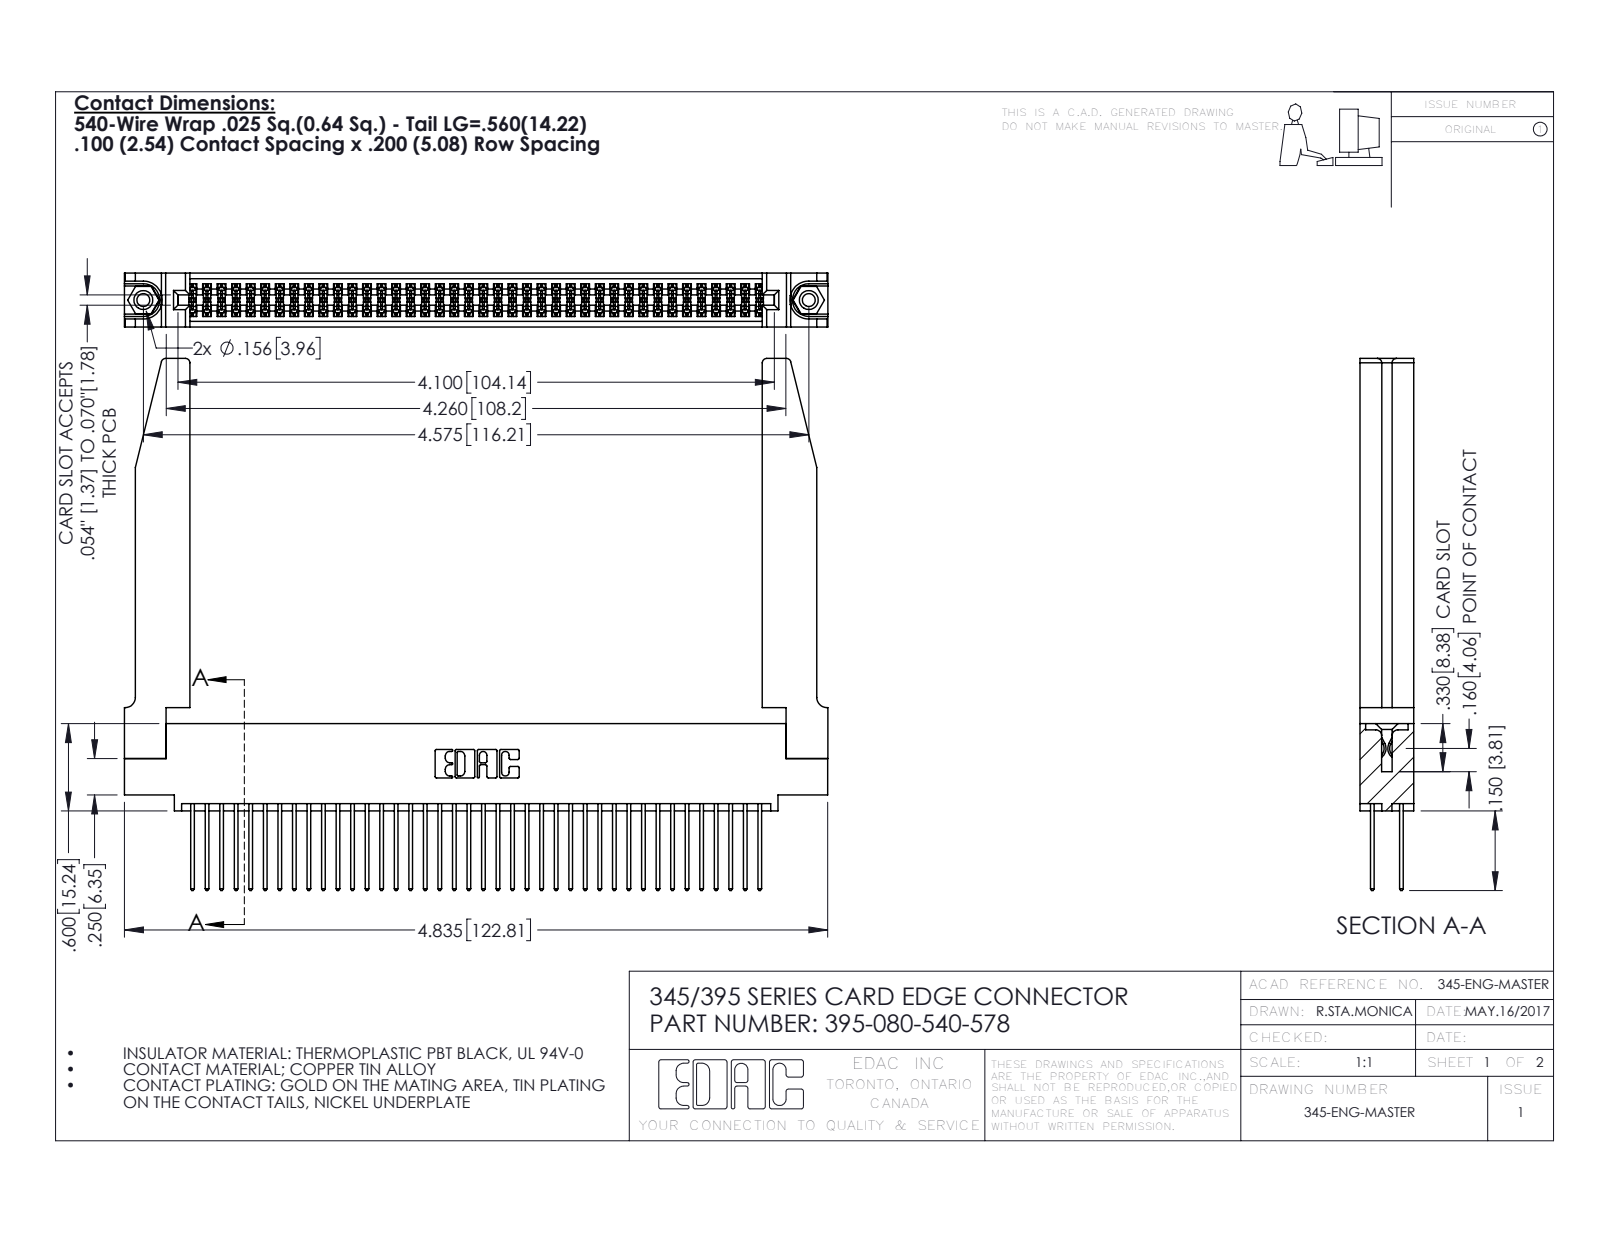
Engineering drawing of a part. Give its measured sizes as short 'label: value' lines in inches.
name: 395-080-540-578; 345 Part_0.110 Offset - 0.156 Dia-TH; 345-220-078_345-220-078; 345-292-001_345-293-140 (+1 more)
written by: SolidWorks 2016 (CONFIG_CONTROL_DESIGN)
unit: in
bodies: 85 solids, 4364 faces (2866 planar, 1446 cylindrical, 52 other)
size: 4.836 × 3.657 × 0.37
volume: 1.215 in³; area: 40.69 in²
holes: 2× ⌀0.089, 2× ⌀0.125, 2× ⌀0.156, 1× ⌀0.064
bosses: 2× ⌀0.155
rounds: 120× R0.006, 80× R0.01, 22× R0.01, 8× R0.03, 6× R0.007, 6× R0.031, 3× R0.026, 2× R0.014
face distances: 0.072, 0.298, 0.37, 0.2, 0.098, 0.272, 0.025, 0.225, 0.175, 0.148
hole spacings: 0.27, 4.339, 4.575
